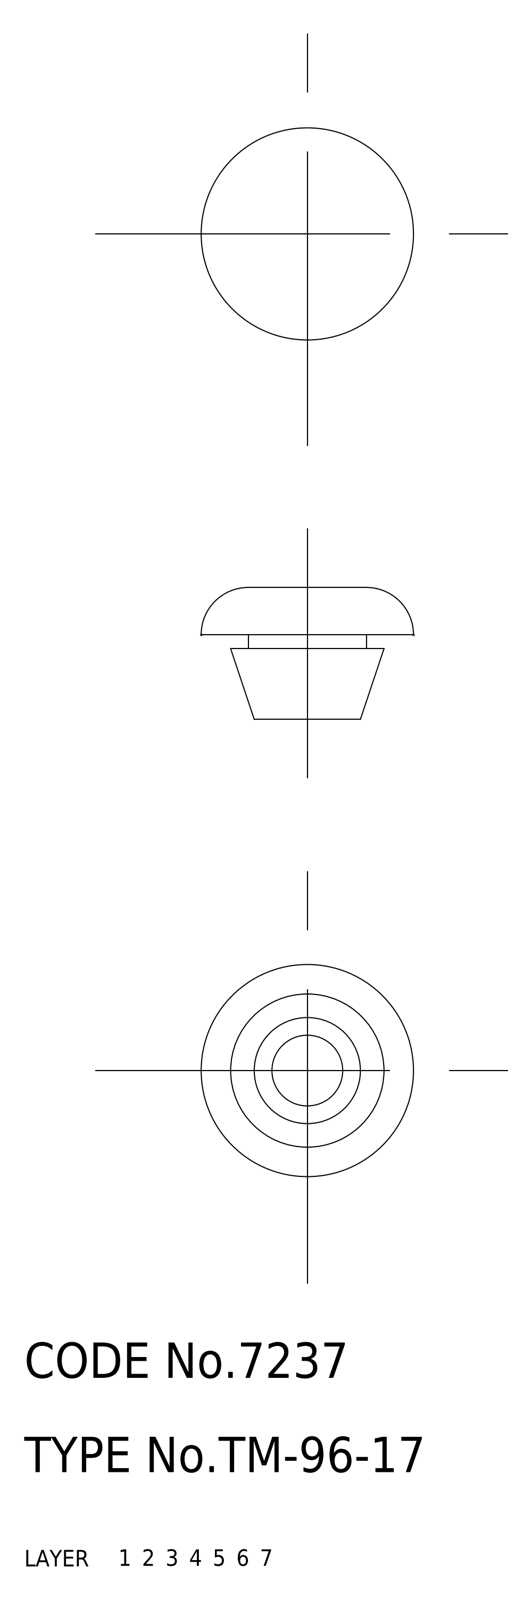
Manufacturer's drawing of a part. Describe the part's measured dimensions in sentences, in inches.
The part is named "cushion". Its 3-D file was written by "CADfix (AUTOMOTIVE_DESIGN)". It is 1 solid with 13 faces: 0 planar, 0 cylindrical and 13 other. Overall it measures 0.709 by 0.709 by 0.441 inches. Its volume is 0.08 cubic inches and its surface area 1.646 square inches.
